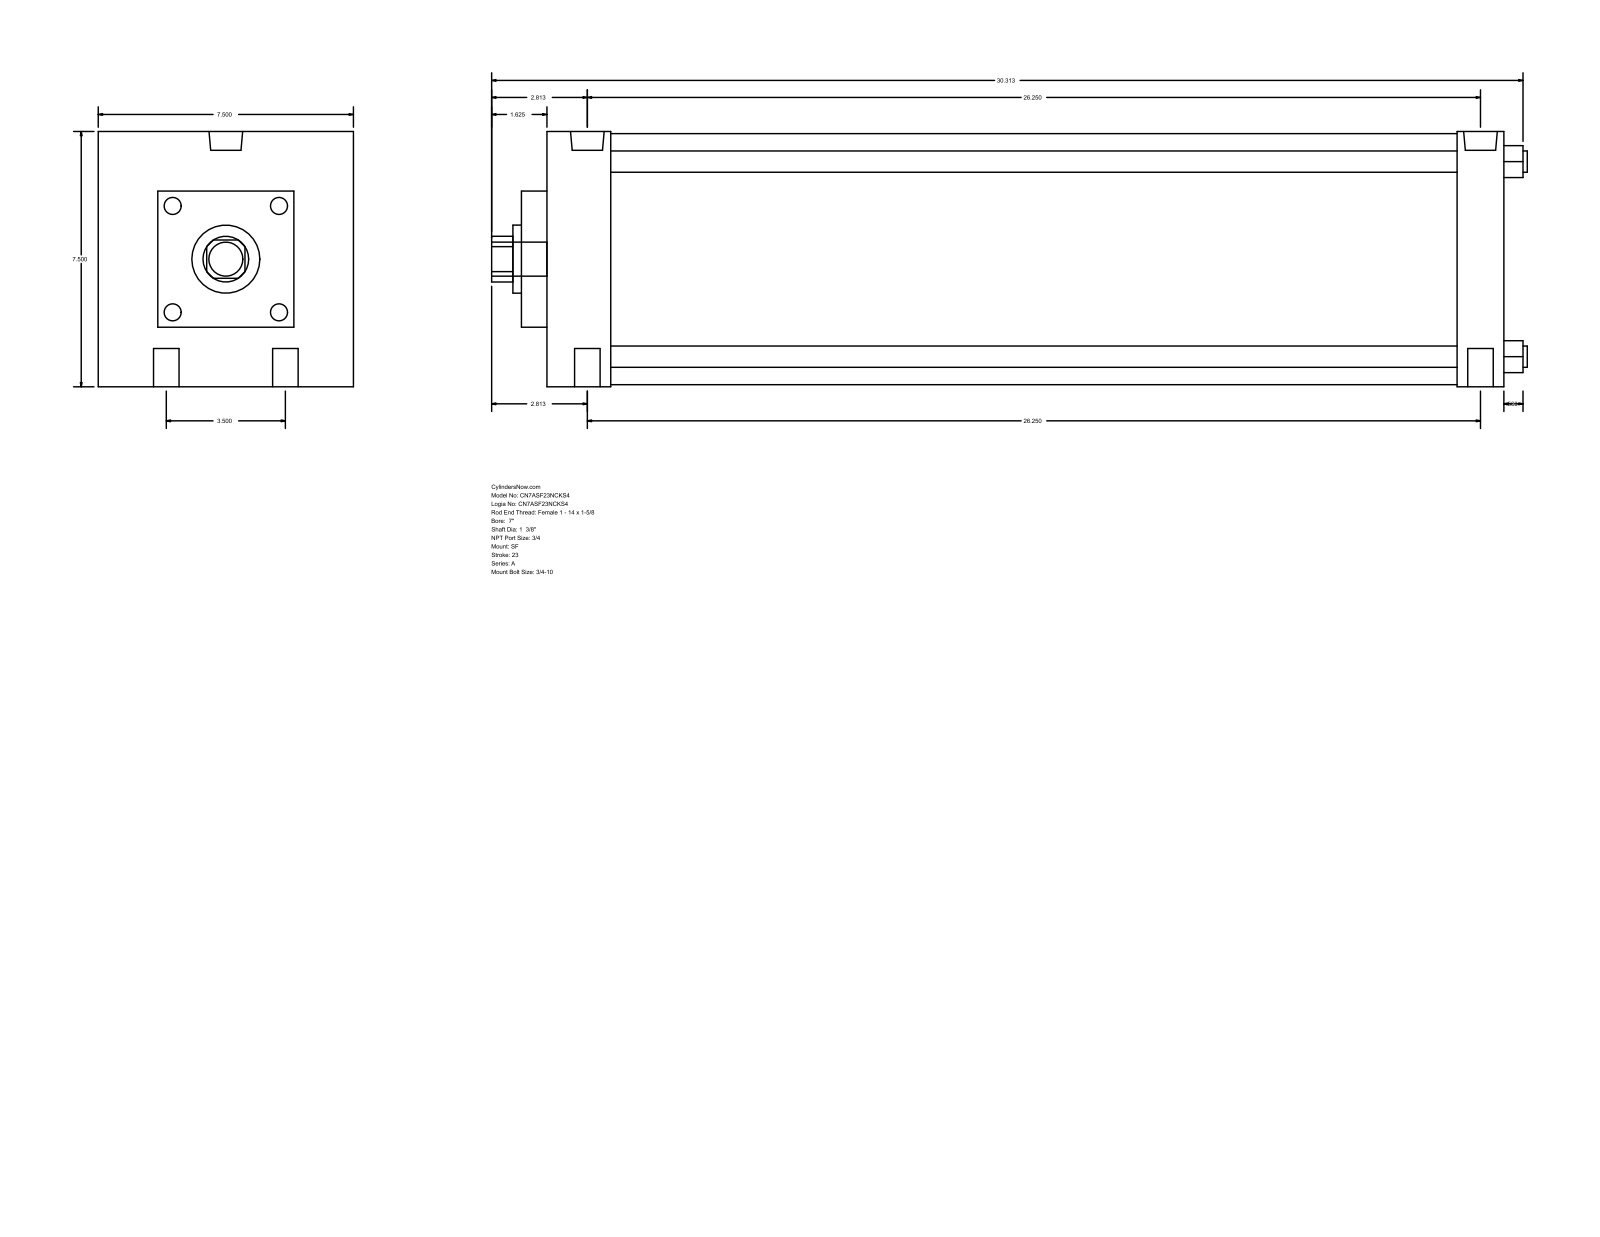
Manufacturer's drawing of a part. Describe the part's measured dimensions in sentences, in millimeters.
The part is named "A_SF__0700_1.375". Its 3-D file was written by "GSSL Pune (CONFIG_CONTROL_DESIGN)". It is 0 solids with 93 faces: 67 planar, 26 cylindrical and 0 other. Overall it measures 773.11 by 190.5 by 190.5 millimeters. Round holes: 4 of diameter 19.05, 2 of diameter 15.08, 2 of diameter 25.12, 1 of diameter 34.92, 1 of diameter 50.8. Round bosses or shafts: 4 of diameter 15.88, 1 of diameter 187.32, 1 of diameter 25.4. Partial cylindrical surfaces (rounded edges, fillets, slot ends): 1 of radius 17.06. The main face-to-face distances are 190.5, 714.38, 19.04, 733.42, 66.67, 698.5, 47.63, 679.46, 631.83, 666.75. The hole center spacings are 44.45, 668.23, 666.75, 88.9, 672.65, 655.63.
